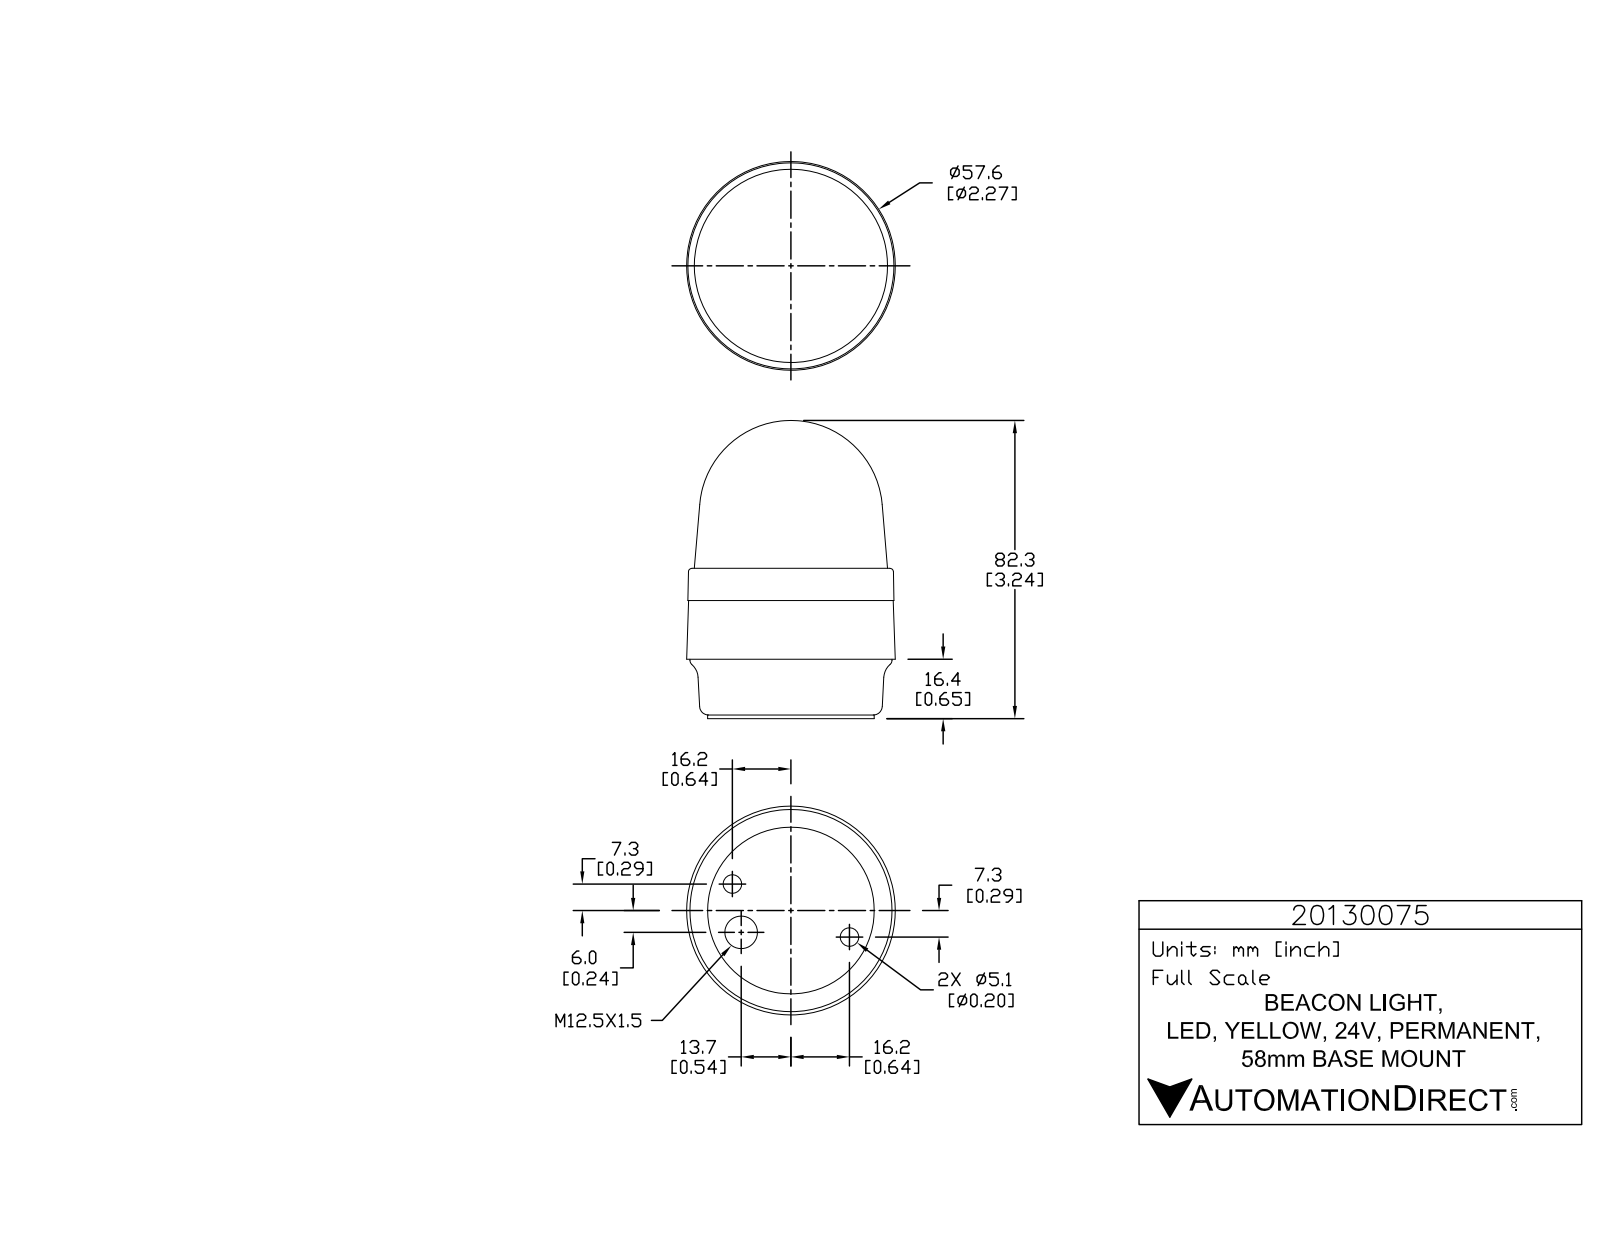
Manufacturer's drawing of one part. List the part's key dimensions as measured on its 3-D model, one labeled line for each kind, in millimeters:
Part name (STEP PRODUCT): 20130075
STEP written by: SolidWorks 2015 (AUTOMOTIVE_DESIGN)
Units: millimetres
Bodies: 1 solid, 763 faces (527 planar, 145 cylindrical, 91 other)
Overall size (bounding box): 82.3 × 57.63 × 57.63
Volume: 164 395 mm³ · Surface area: 16 261 mm²
Round holes (diameter × count): ⌀0.99 ×3, ⌀5.11 ×2, ⌀9 ×1
Round bosses / shafts (diameter × count): ⌀5.74 ×3, ⌀1.43 ×3, ⌀55.8 ×1, ⌀46 ×1
Partial cylindrical surfaces — rounded edges, fillets, slot ends (radius × count): R0.2 ×6, R0.21 ×6, R0.21 ×6, R3.32 ×6, R0.1 ×3, R0.12 ×3, R0.19 ×3, R0.2 ×3
Main face-to-face distances: 16.4, 1, 15.4, 41.5, 40.5, 25.1, 32.6, 31.6, 16.2, 8.9
Hole centre spacings: 13.56, 29.94, 35.5
